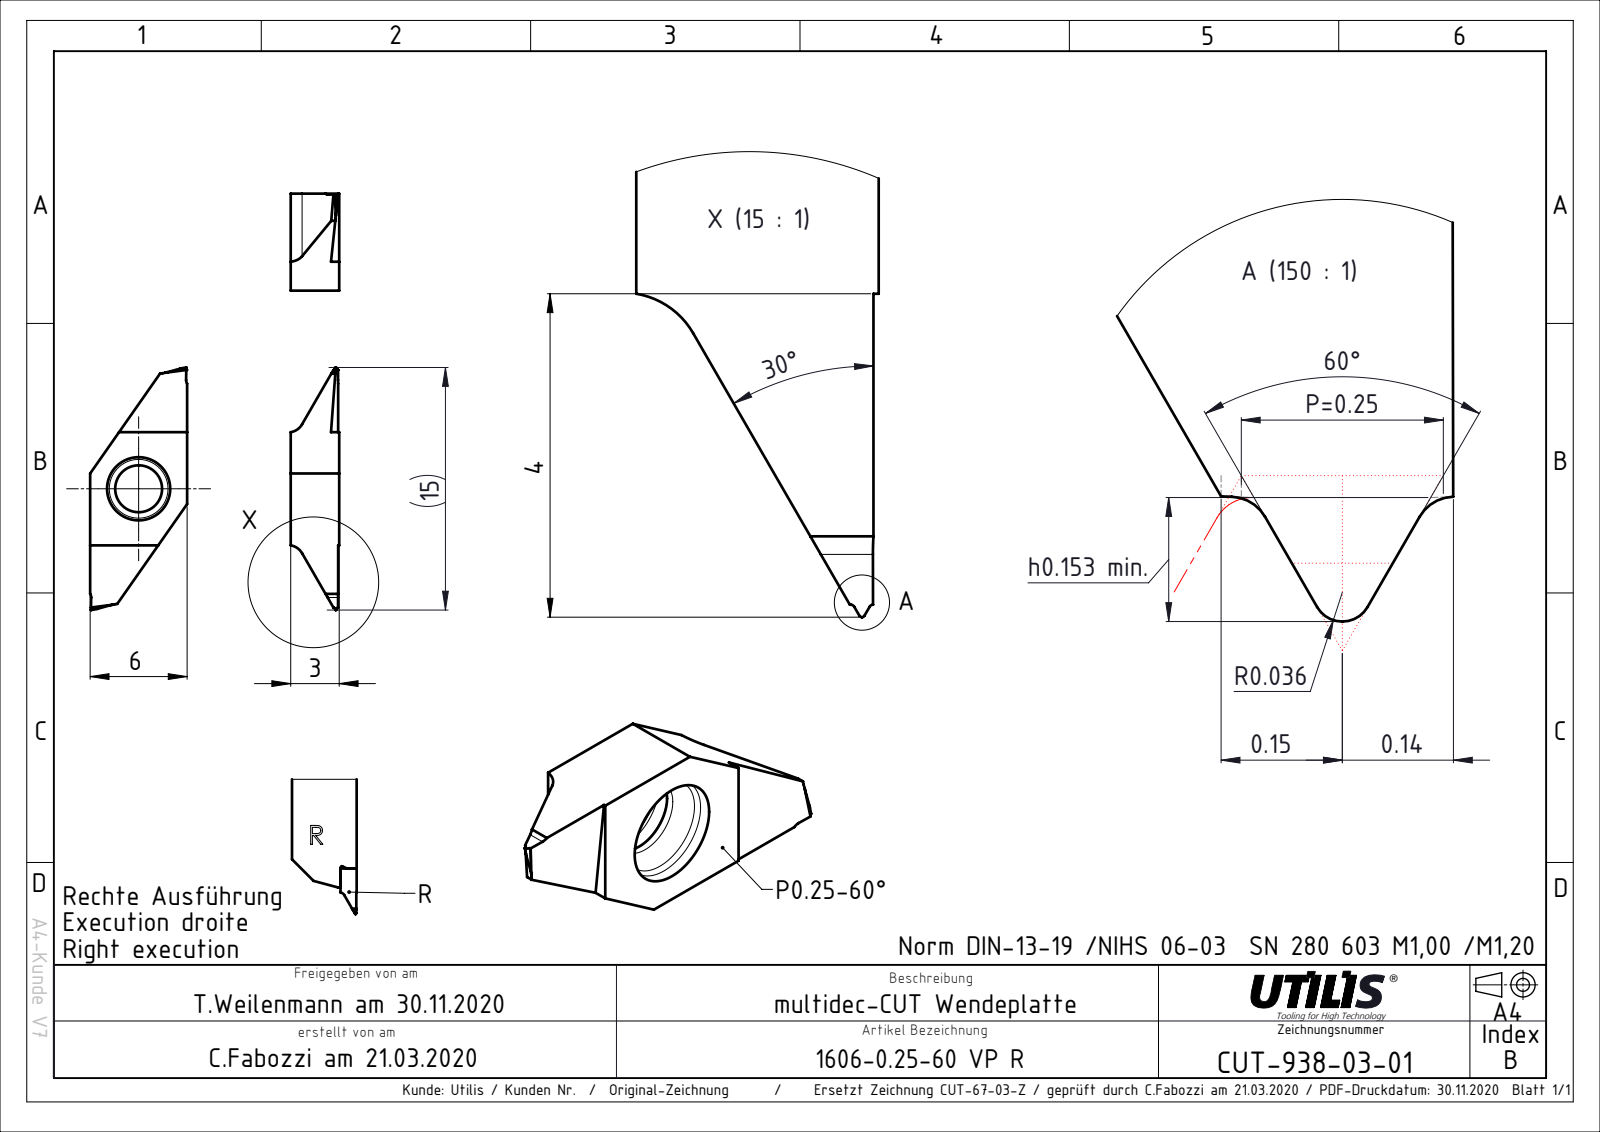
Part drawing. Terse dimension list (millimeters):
name: CUT-938-03; ASME Y14.5
written by: FormatWorks Professional (AP242_MANAGED_MODEL_BASED_3D_ENGINEERING_MIM_LF)
unit: mm
bodies: 1 solid, 40 faces (22 planar, 14 cylindrical, 4 other)
size: 15 × 6 × 3
volume: 127 mm³; area: 210 mm²
holes: 1× ⌀2.9
rounds: 2× R1
face distances: 6, 3, 9, 12, 7, 11.14, 11.15, 13.21, 13.22
